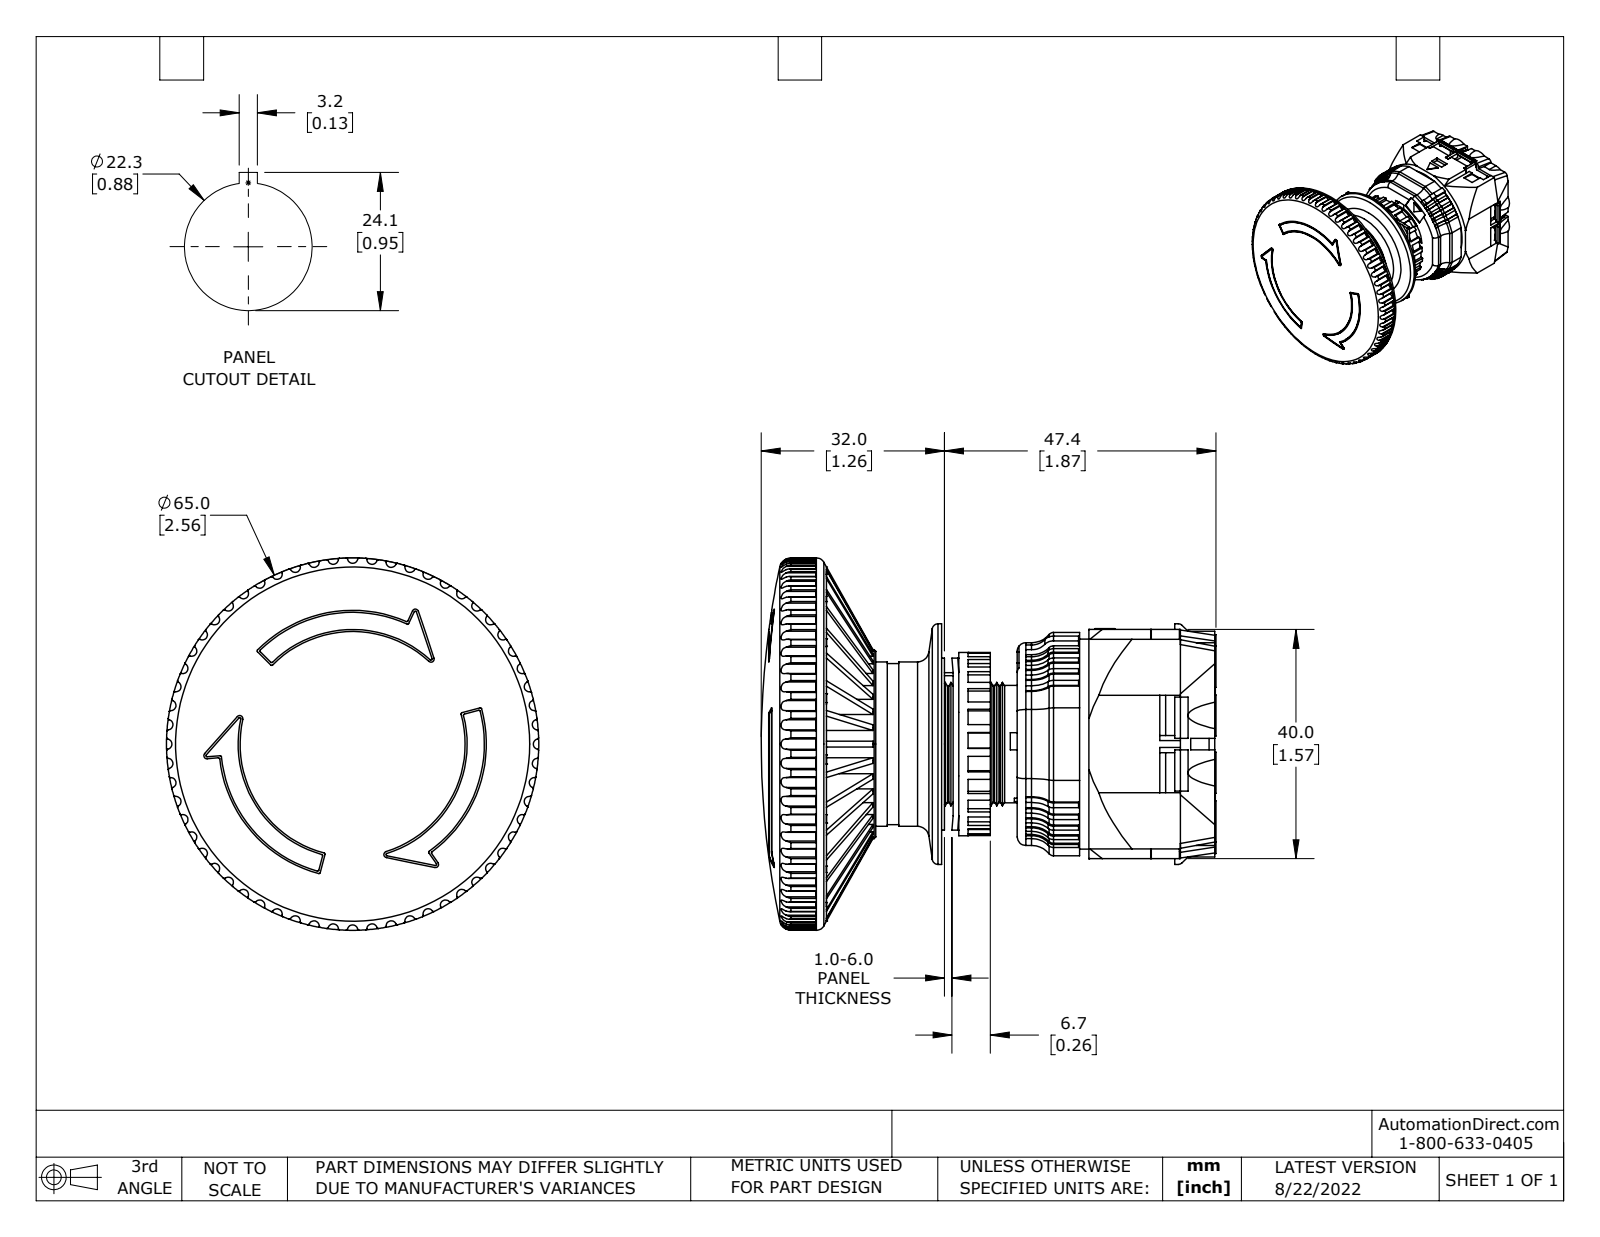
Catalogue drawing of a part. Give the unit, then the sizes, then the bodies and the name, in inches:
Units: inches
Overall size (bounding box): 3.123 × 2.559 × 2.559
Round holes (diameter × count): ⌀0.138 ×12, ⌀0.244 ×12, ⌀0.13 ×2, ⌀0.276 ×1, ⌀0.315 ×1, ⌀0.689 ×1, ⌀0.827 ×1, ⌀0.839 ×1, ⌀0.866 ×1, ⌀0.878 ×1, ⌀1.102 ×1, ⌀1.106 ×1
Round bosses / shafts (diameter × count): ⌀0.283 ×12, ⌀2.559 ×1, ⌀1.654 ×1, ⌀1.299 ×1, ⌀1.26 ×1, ⌀1.181 ×1, ⌀1.13 ×1, ⌀0.882 ×1
Partial cylindrical surfaces — rounded edges, fillets, slot ends (radius × count): R0.008 ×146, R0.035 ×62, R0.039 ×29, R0.049 ×19, R0.148 ×19, R1.249 ×18, R0.059 ×12, R0.165 ×12
Main face-to-face distances: 0.039, 0.394, 0.315, 0.453, 0.339, 1.421, 0.866, 0.709, 0.488, 0.846
Hole centre spacings: 0.641, 0.907, 0.325, 0.349, 0.394, 0.585, 0.713, 0.735
Volume: 4.334 in³ · Surface area: 95.13 in²
Bodies: 26 solids, 2720 faces (1757 planar, 782 cylindrical, 181 other)
Part name (STEP PRODUCT): AR22VPR-01R
STEP written by: SolidWorks 2021 (CONFIG_CONTROL_DESIGN)
